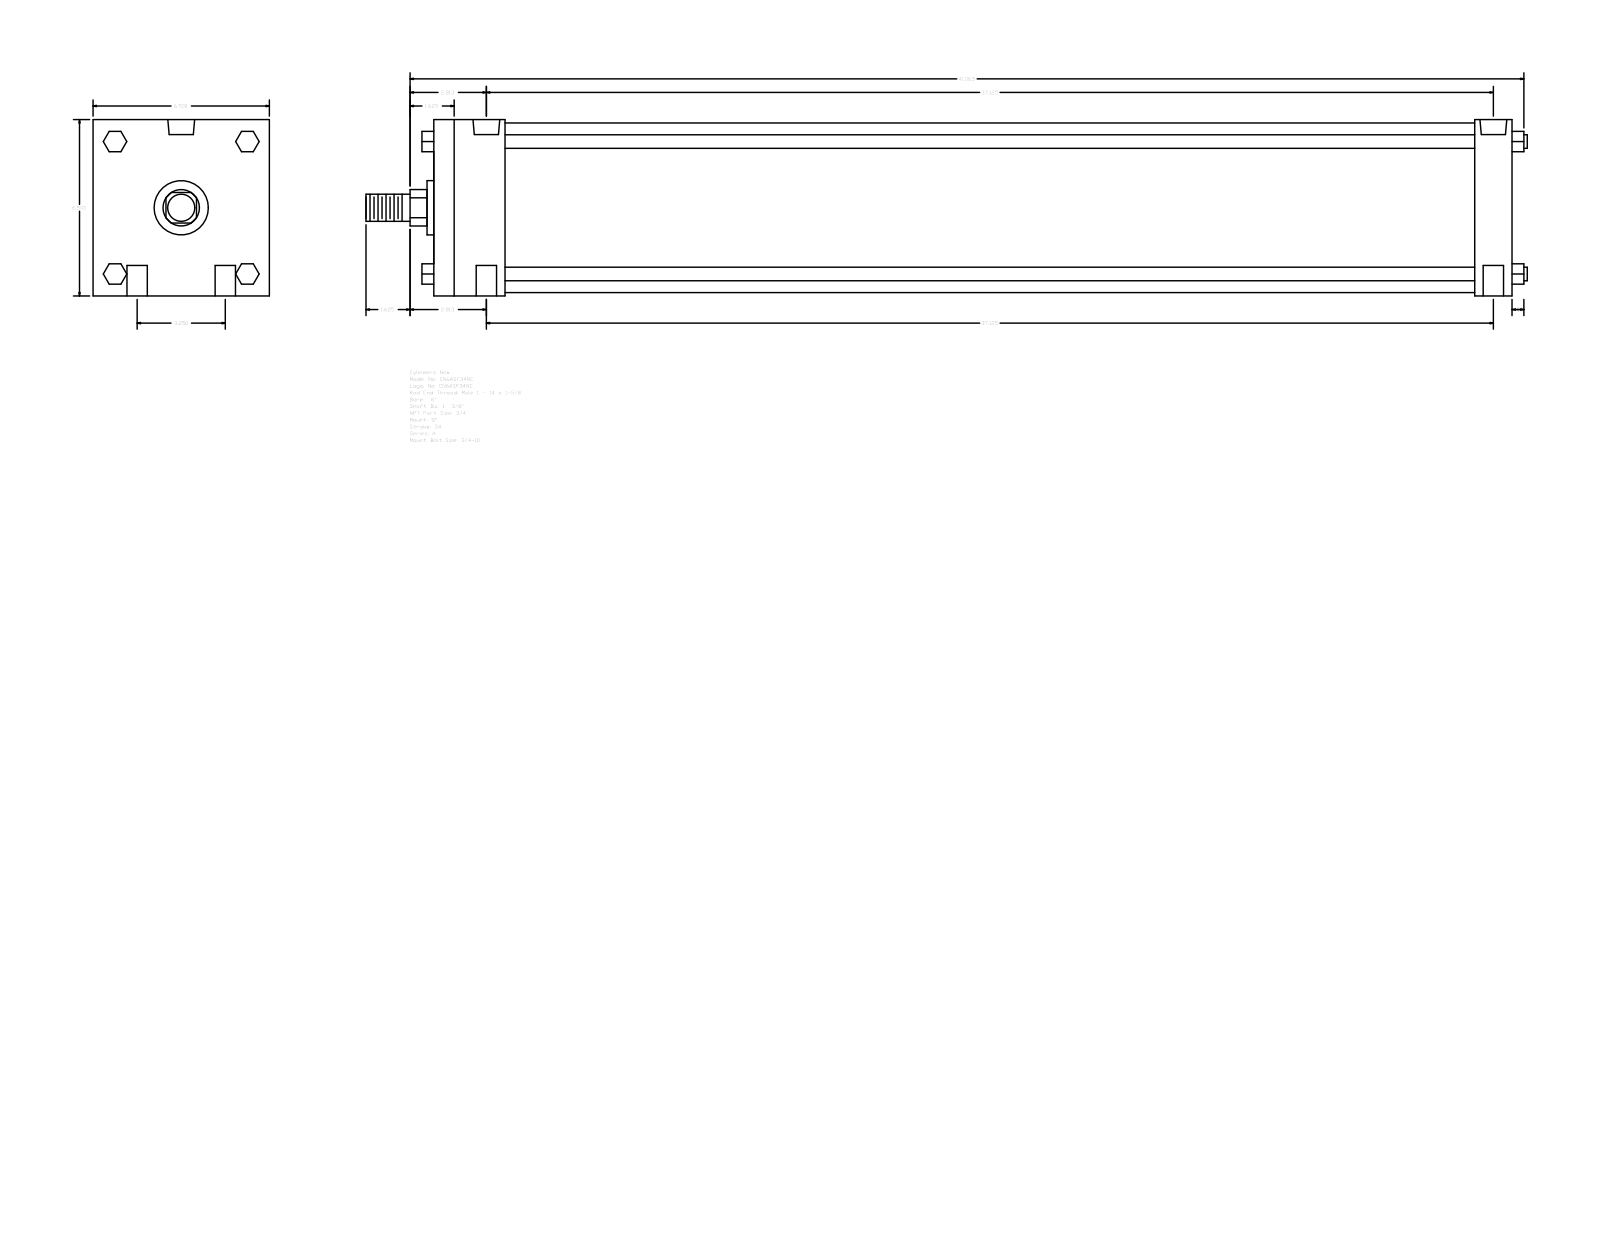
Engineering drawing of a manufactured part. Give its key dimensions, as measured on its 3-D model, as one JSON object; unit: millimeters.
{"part_name": "A_SF__0600_1.375", "step_written_by": "GSSL Pune (CONFIG_CONTROL_DESIGN)", "units": "millimeters", "bodies": {"solids": 0, "faces": 124, "planar": 94, "cylindrical": 30, "other": 0}, "overall_size": [1087.44, 165.1, 165.1], "round_holes": [[19.05, 4], [15.08, 2], [25.12, 2]], "round_bosses_or_shafts": [[12.7, 4], [158.75, 1], [50.8, 1], [34.92, 1], [25.4, 1]], "partial_cylinders_radius": [[17.06, 1]], "face_to_face_distances": [165.1, 1009.65, 974.72, 34.93, 66.67, 908.05, 942.98, 19.05, 61.97, 107.34], "hole_center_spacings": [41.27, 943.87, 942.97, 82.54, 946.58, 931.85]}
